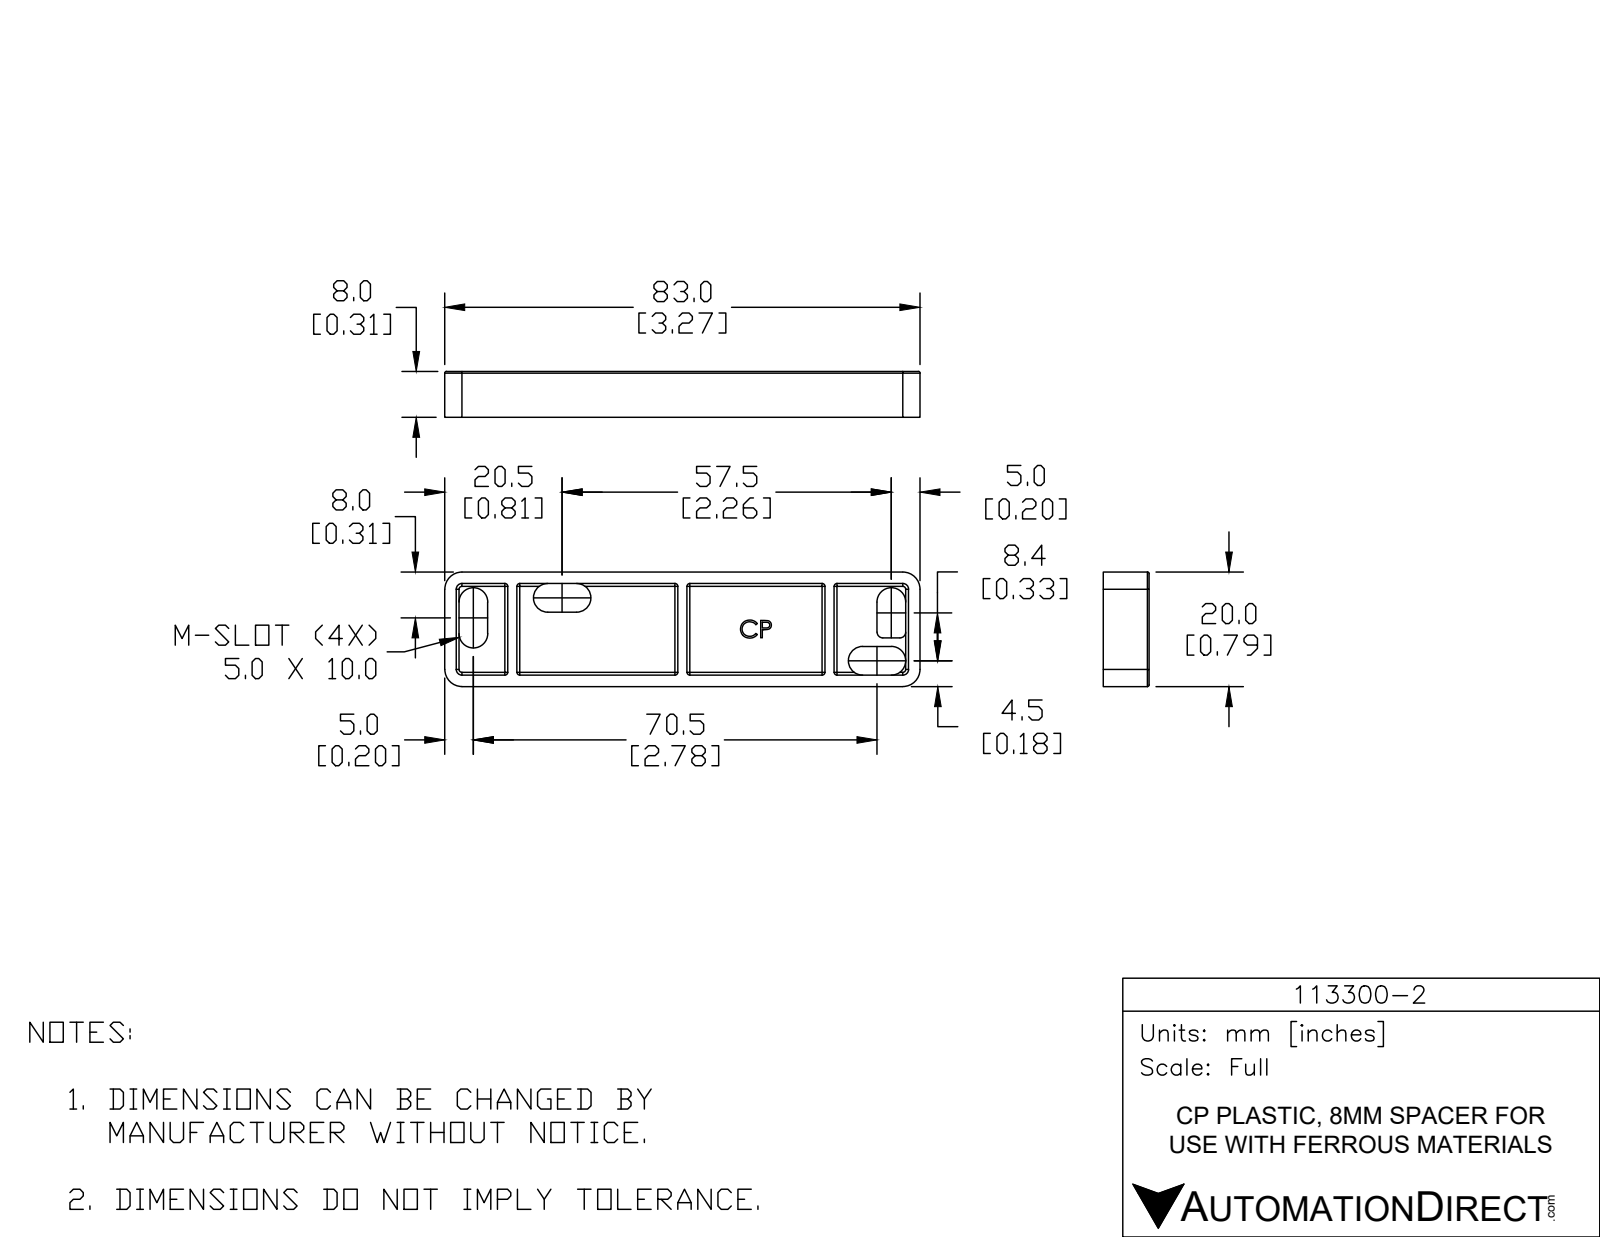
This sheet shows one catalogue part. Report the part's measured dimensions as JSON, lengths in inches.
{"part_name": "113-CP Spacer", "step_written_by": "SolidWorks 2018 (CONFIG_CONTROL_DESIGN)", "units": "inches", "bodies": {"solids": 1, "faces": 155, "planar": 56, "cylindrical": 53, "other": 46}, "overall_size": [3.268, 0.787, 0.315], "volume_in3": 0.412, "surface_area_in2": 9.492, "partial_cylinders_radius": [[0.02, 22], [0.098, 7], [0.039, 6], [0.012, 4], [0.118, 4]], "face_to_face_distances": [0.118, 0.079, 0.709, 0.787, 0.197, 0.315, 0.63, 0.063, 1.602, 1.665]}
